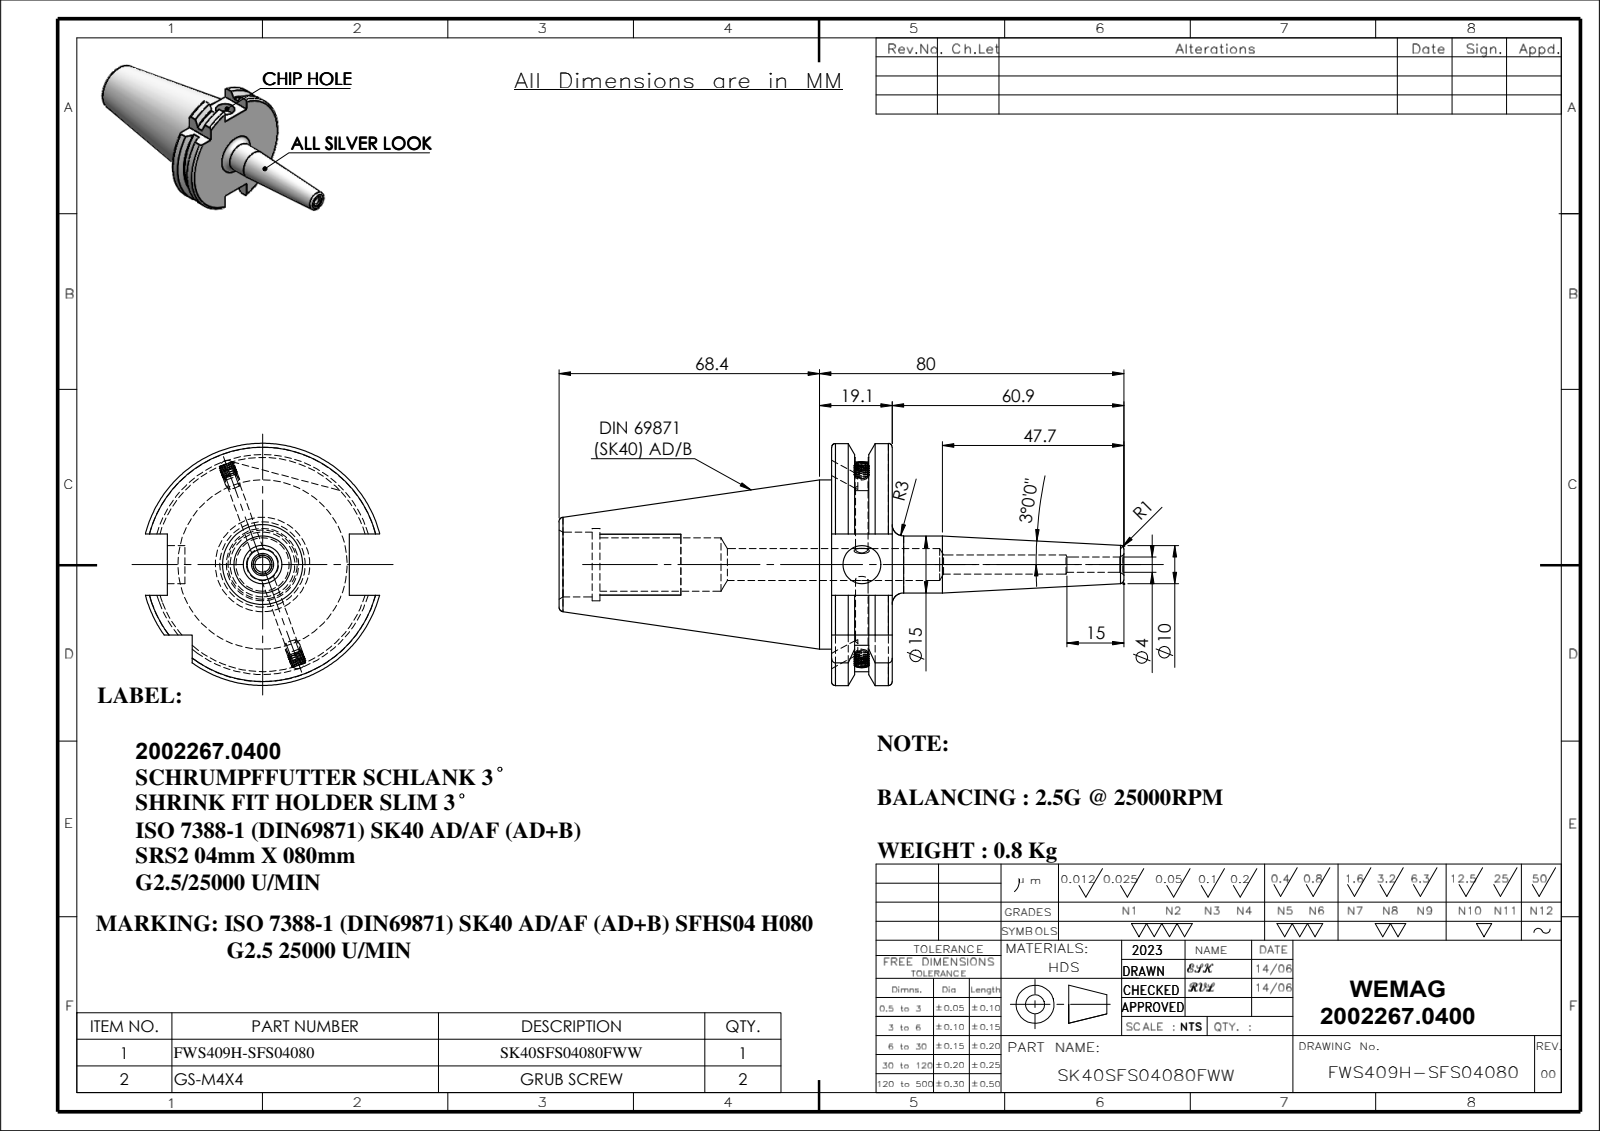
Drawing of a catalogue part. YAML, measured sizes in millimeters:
part_name: "91406-SRS204080; SK40SFS04080FWW; GS-M4X4_DIN 913 - M4 x 4-N"
step_written_by: "SolidWorks 2018 (CONFIG_CONTROL_DESIGN)"
units: millimeters
bodies: {solids: 3, faces: 198, planar: 46, cylindrical: 54, other: 98}
overall_size: [148.4, 63.55, 61.48]
volume: 109480
surface_area: 24333
round_holes:
  - {diameter: 3.3, count: 1}
  - {diameter: 4, count: 1}
  - {diameter: 5, count: 1}
  - {diameter: 8.4, count: 1}
  - {diameter: 10, count: 1}
  - {diameter: 14, count: 1}
  - {diameter: 17, count: 1}
  - {diameter: 19, count: 1}
round_bosses_or_shafts:
  - {diameter: 4, count: 2}
  - {diameter: 44.45, count: 1}
  - {diameter: 15, count: 1}
partial_cylinders:
  - {radius: 28.12, count: 1}
  - {radius: 31.77, count: 1}
face_to_face_distances: [15.9, 16.1, 47.8, 60.9, 76.8, 71.6, 87.5, 10.7, 77.63, 66.93]
